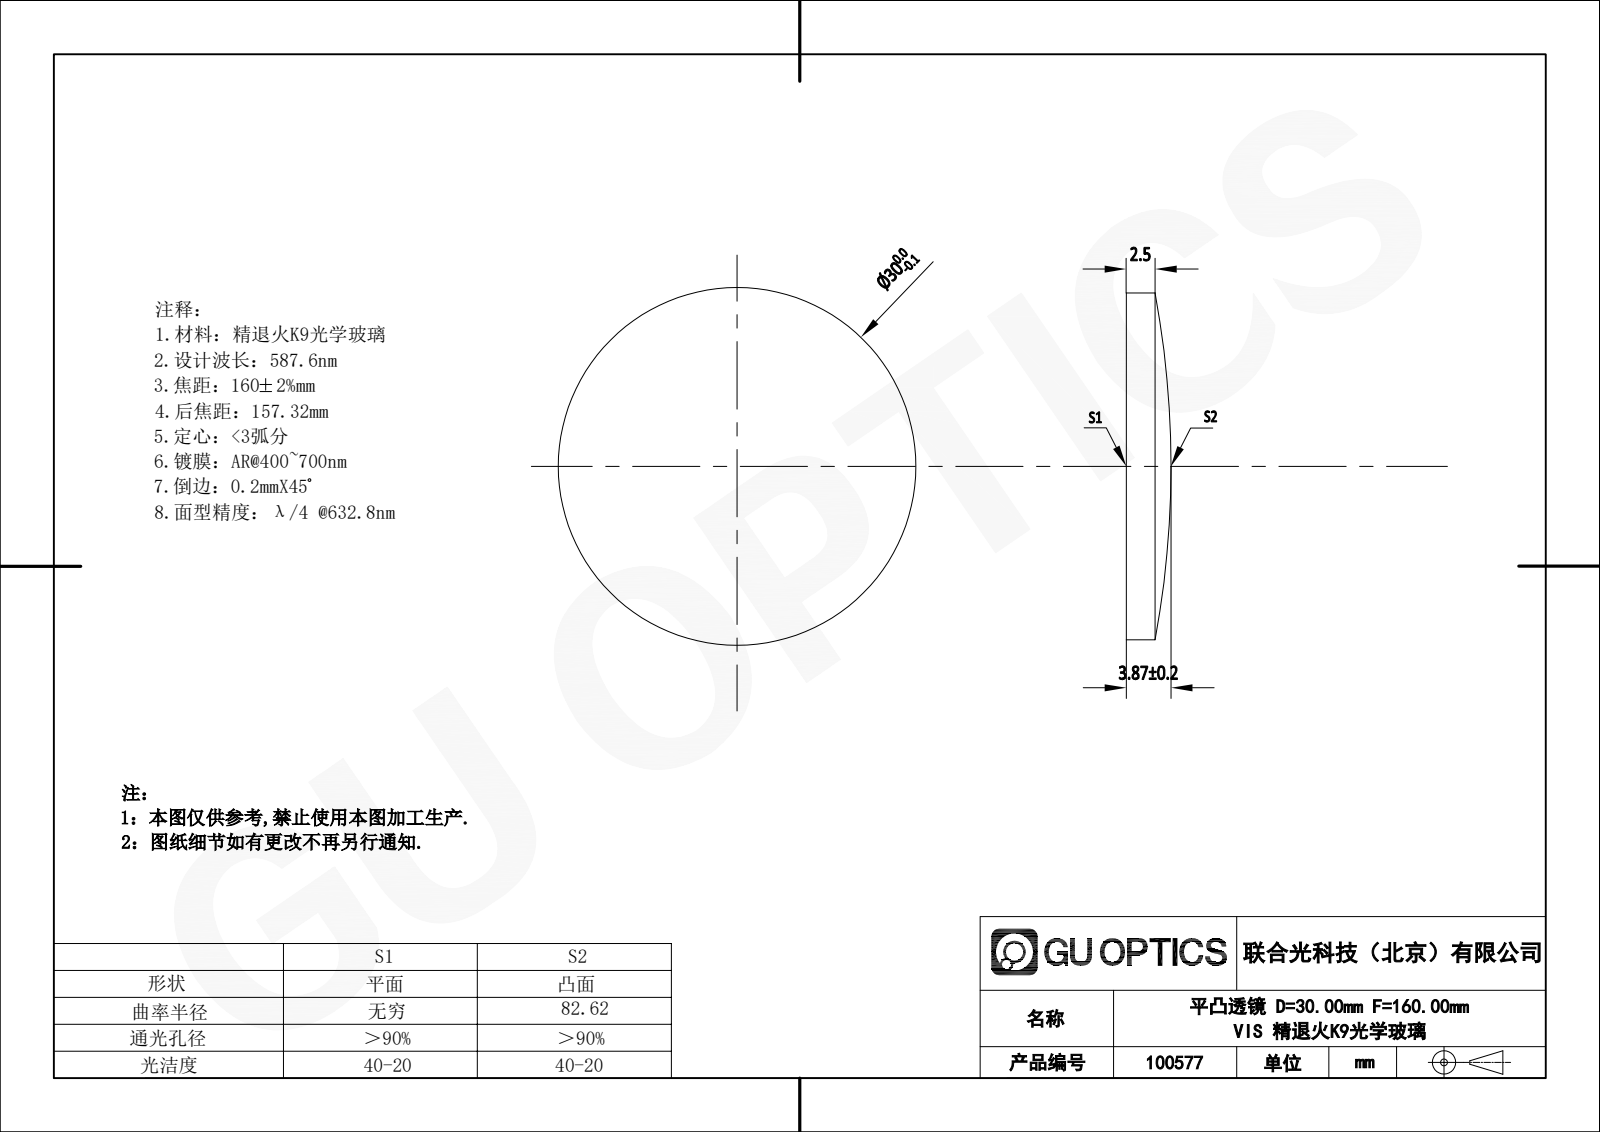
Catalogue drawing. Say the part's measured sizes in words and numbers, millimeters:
The part is named "100577". Its 3-D file was written by "SolidWorks 2020 (CONFIG_CONTROL_DESIGN)". It is 1 solid with 5 faces: 1 planar, 2 cylindrical and 2 other. Overall it measures 30 by 30 by 3.6 millimeters. Its volume is 2 156 cubic millimeters and its surface area 1 653 square millimeters. Round bosses or shafts: 1 of diameter 30.
